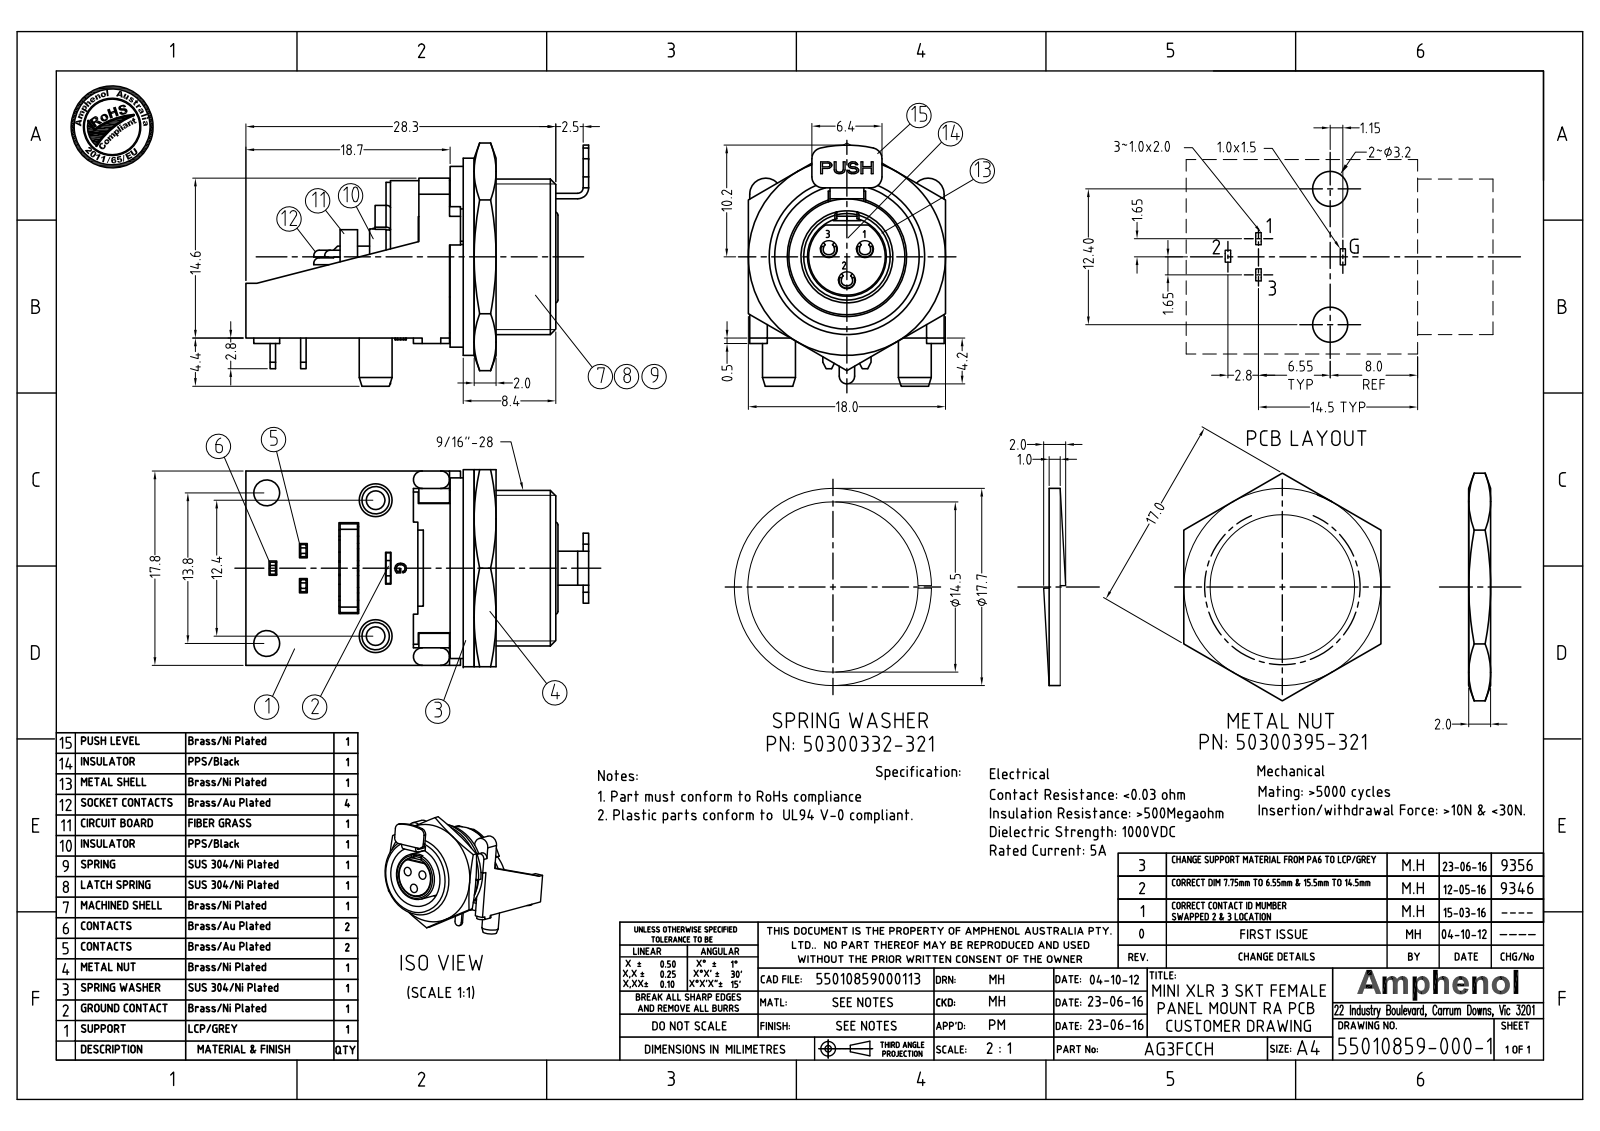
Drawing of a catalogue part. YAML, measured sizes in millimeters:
part_name: "AG3FCCH_Shrinkwrap_1"
step_written_by: "Autodesk Inventor 2012 (AUTOMOTIVE_DESIGN)"
units: millimeters
bodies: {solids: 0, faces: 320, planar: 171, cylindrical: 104, other: 45}
overall_size: [37, 21.8, 20.6]
round_holes:
  - {diameter: 1.5, count: 6}
  - {diameter: 1.2, count: 3}
  - {diameter: 1.7, count: 2}
  - {diameter: 0.8, count: 1}
  - {diameter: 8.6, count: 1}
  - {diameter: 10.9, count: 1}
  - {diameter: 11, count: 1}
round_bosses_or_shafts:
  - {diameter: 3, count: 2}
  - {diameter: 16.8, count: 1}
  - {diameter: 14.2, count: 1}
  - {diameter: 14, count: 1}
  - {diameter: 9.9, count: 1}
  - {diameter: 8.5, count: 1}
  - {diameter: 7, count: 1}
partial_cylinders:
  - {radius: 0.1, count: 19}
  - {radius: 0.5, count: 8}
  - {radius: 0.3, count: 6}
  - {radius: 1, count: 6}
  - {radius: 1.2, count: 4}
  - {radius: 0.7, count: 2}
  - {radius: 0.8, count: 2}
  - {radius: 1.5, count: 2}
face_to_face_distances: [1.6, 15, 0.4, 16.6, 3.4, 10, 2.5, 11, 2.5, 5.4]
hole_center_spacings: [3.3, 3.3, 1.8, 1.8, 1.8, 2.1, 2.1, 2.2]
